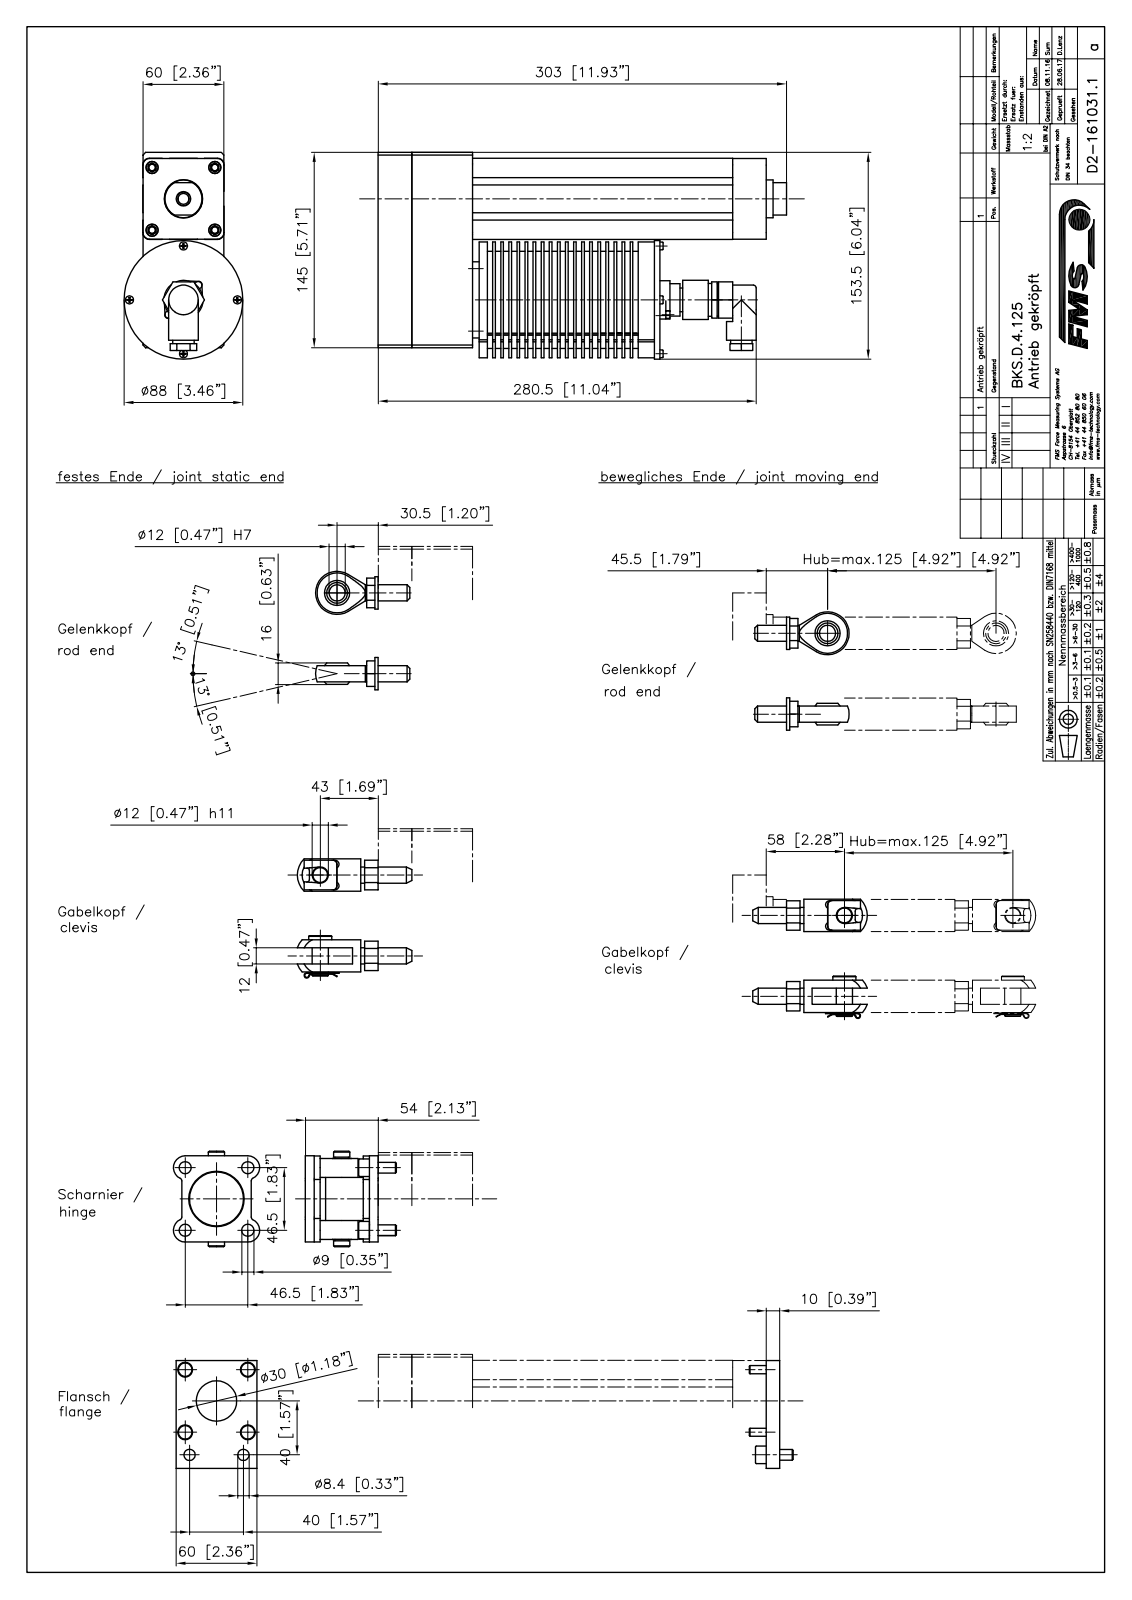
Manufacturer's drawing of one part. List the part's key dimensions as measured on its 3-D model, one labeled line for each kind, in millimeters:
Part name (STEP PRODUCT): K1610311_STP; K1309121; K0702222; K0711168 (+8 more)
STEP written by: Mechanical Desktop 2009 (CONFIG_CONTROL_DESIGN)
Units: millimetres
Bodies: 29 solids, 1266 faces (585 planar, 512 cylindrical, 169 other)
Overall size (bounding box): 396 × 153.5 × 88
Volume: 1 298 000 mm³ · Surface area: 442 426 mm²
Round holes (diameter × count): ⌀2.6 ×10, ⌀3.42 ×8, ⌀5.15 ×8, ⌀5 ×5, ⌀4 ×4, ⌀6.3 ×4, ⌀6.4 ×4, ⌀6.65 ×4, ⌀6.91 ×4, ⌀9 ×4, ⌀2.14 ×3, ⌀3.6 ×2
Round bosses / shafts (diameter × count): ⌀2.15 ×7, ⌀3 ×6, ⌀10 ×4, ⌀6 ×4, ⌀24 ×2, ⌀5.5 ×2, ⌀88 ×1, ⌀86 ×1
Partial cylindrical surfaces — rounded edges, fillets, slot ends (radius × count): R5 ×18, R0.5 ×14, R8 ×8, R2 ×6, R3 ×6, R20 ×5, R1.75 ×4, R4.5 ×4
Main face-to-face distances: 60.15, 70, 60.3, 60, 1.95, 58.35, 1.8, 58.2, 4, 56.4
Hole centre spacings: 28.73, 67.77, 32.88, 7.63, 21.82, 29.83, 30, 33.3
